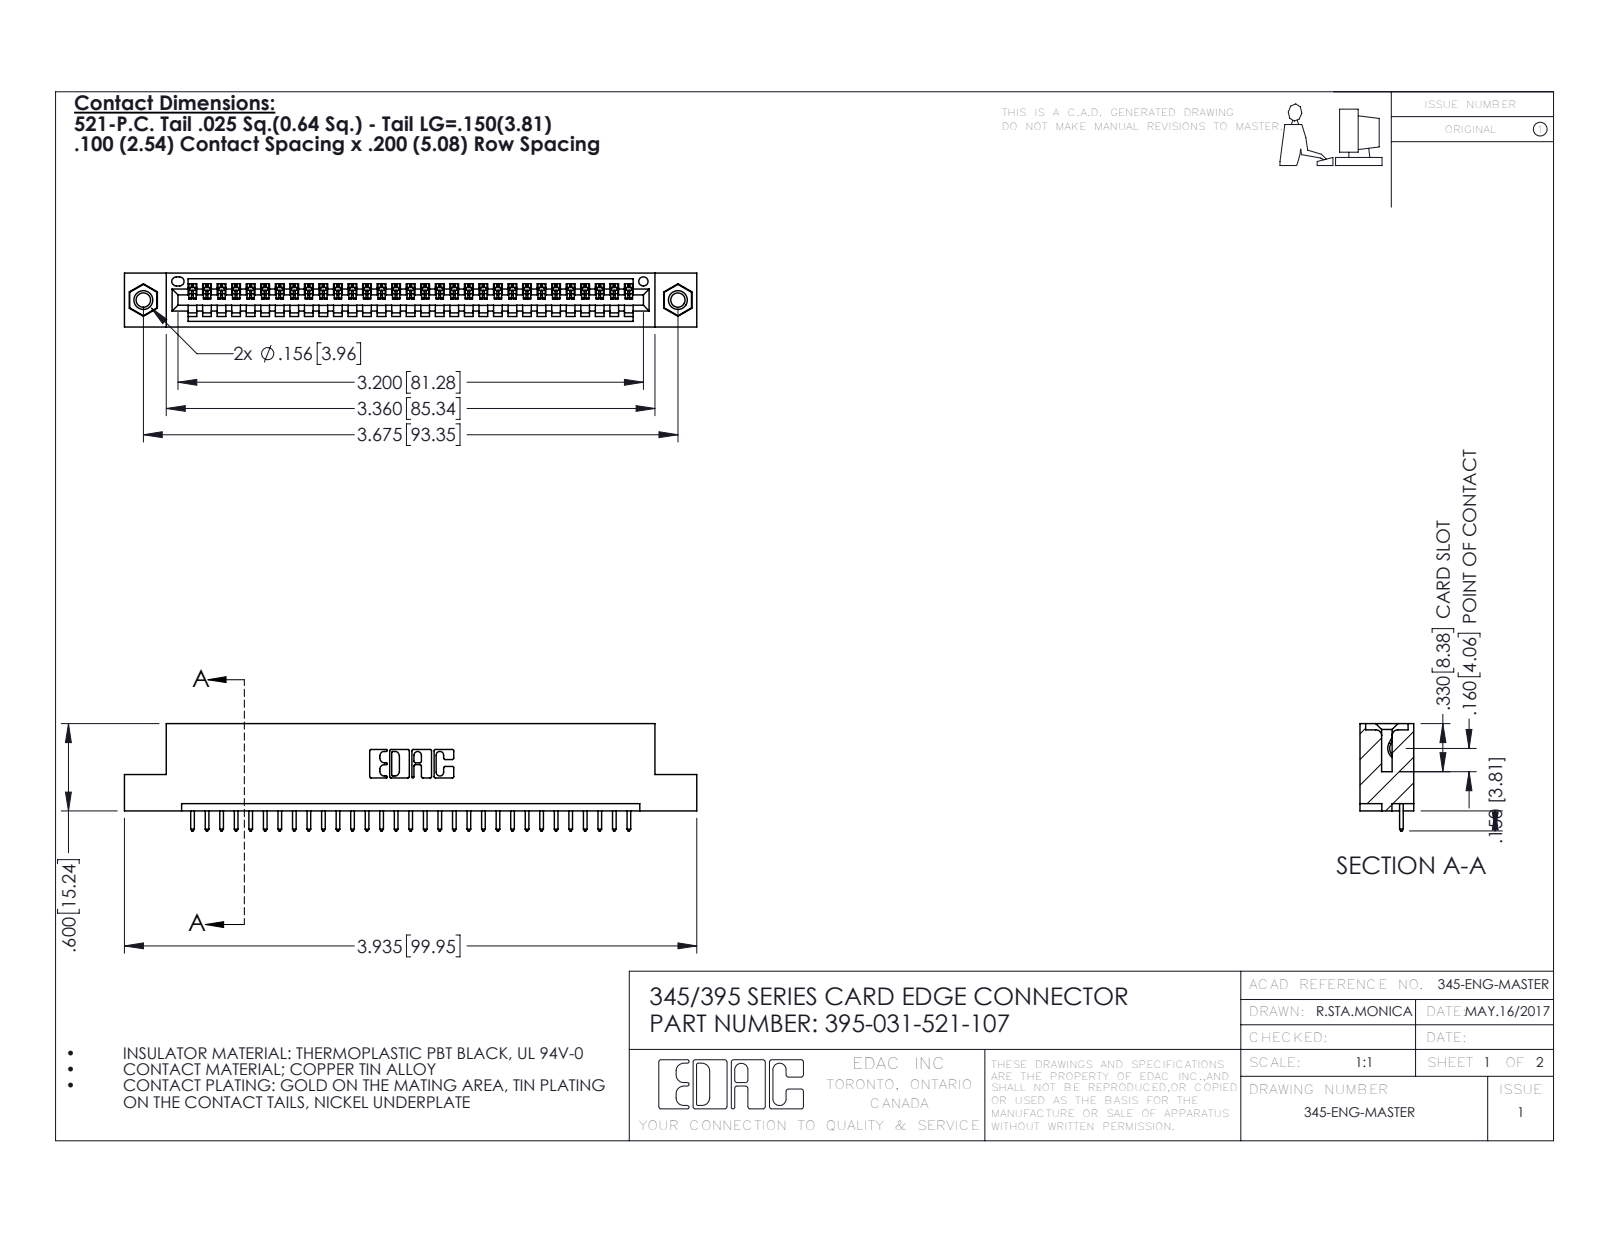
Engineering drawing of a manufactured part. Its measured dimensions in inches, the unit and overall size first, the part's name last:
Units: inches
Overall size (bounding box): 3.935 × 0.737 × 0.37
Round holes (diameter × count): ⌀0.098 ×2, ⌀0.125 ×2, ⌀0.156 ×2, ⌀0.064 ×1
Round bosses / shafts (diameter × count): ⌀0.155 ×2
Partial cylindrical surfaces — rounded edges, fillets, slot ends (radius × count): R0.006 ×62, R0.01 ×62, R0.01 ×22, R0.007 ×6, R0.031 ×6, R0.026 ×3, R0.031 ×2, R0.04 ×2
Main face-to-face distances: 0.072, 0.298, 0.2, 0.37, 0.098, 0.272, 0.025, 0.225, 0.149, 0.072
Hole centre spacings: 0.27, 3.44, 3.675
Volume: 0.568 in³ · Surface area: 18.44 in²
Bodies: 34 solids, 1984 faces (1352 planar, 616 cylindrical, 16 other)
Part name (STEP PRODUCT): 345-250-001_345-250-005-103; 395-031-521-107; 345 Part_Flush Mounting Lugs - 0.156 Dia-TI; 345-292-001_345-293-121
STEP written by: SolidWorks 2016 (CONFIG_CONTROL_DESIGN)
